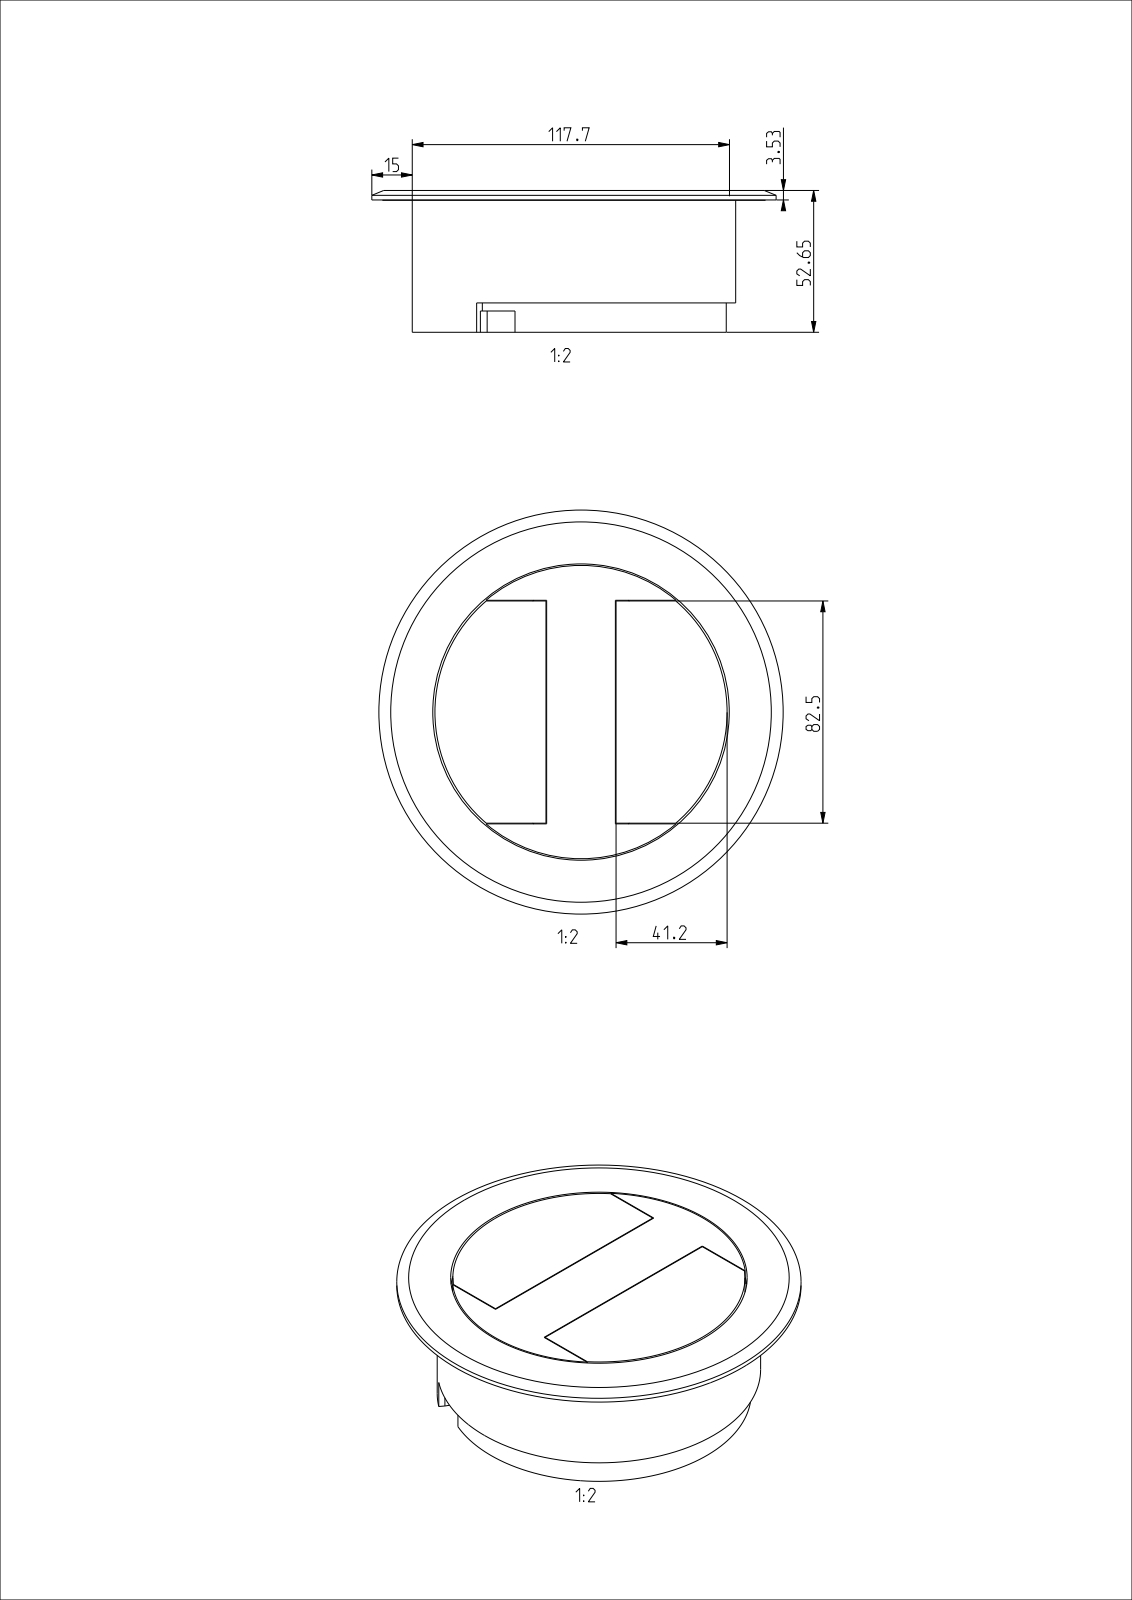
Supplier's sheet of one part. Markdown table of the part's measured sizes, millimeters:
| quantity | value |
| --- | --- |
| part name | BSR_BECHEROBERTEIL; BSR_DECKEL_KUNSTSTOFFKLAPPE; LAR02KK_ASM |
| STEP written by | CREO PARAMETRIC BY PTC INC, 2022024 (AUTOMOTIVE_DESIGN) |
| units | millimeters |
| bodies | 2 solids, 115 faces (87 planar, 26 cylindrical, 2 other) |
| overall size | 150 × 150 × 52.65 |
| volume | 170 048 mm³ |
| surface area | 111 193 mm² |
| round holes (diameter × count) | 90 × 1, 110 × 1, 115.4 × 1, 144.4 × 1 |
| round bosses / shafts (diameter × count) | 150 × 1, 142 × 1, 120 × 1, 115.02 × 1 |
| partial cylindrical surfaces (radius × count) | 53 × 1, 54.2 × 1, 54.45 × 1, 55 × 1, 56.5 × 1 |
| main face-to-face distances | 2.25, 3.75, 6, 2.35, 1.4, 3.65, 6.3, 8.65, 10.05, 12.3 |
